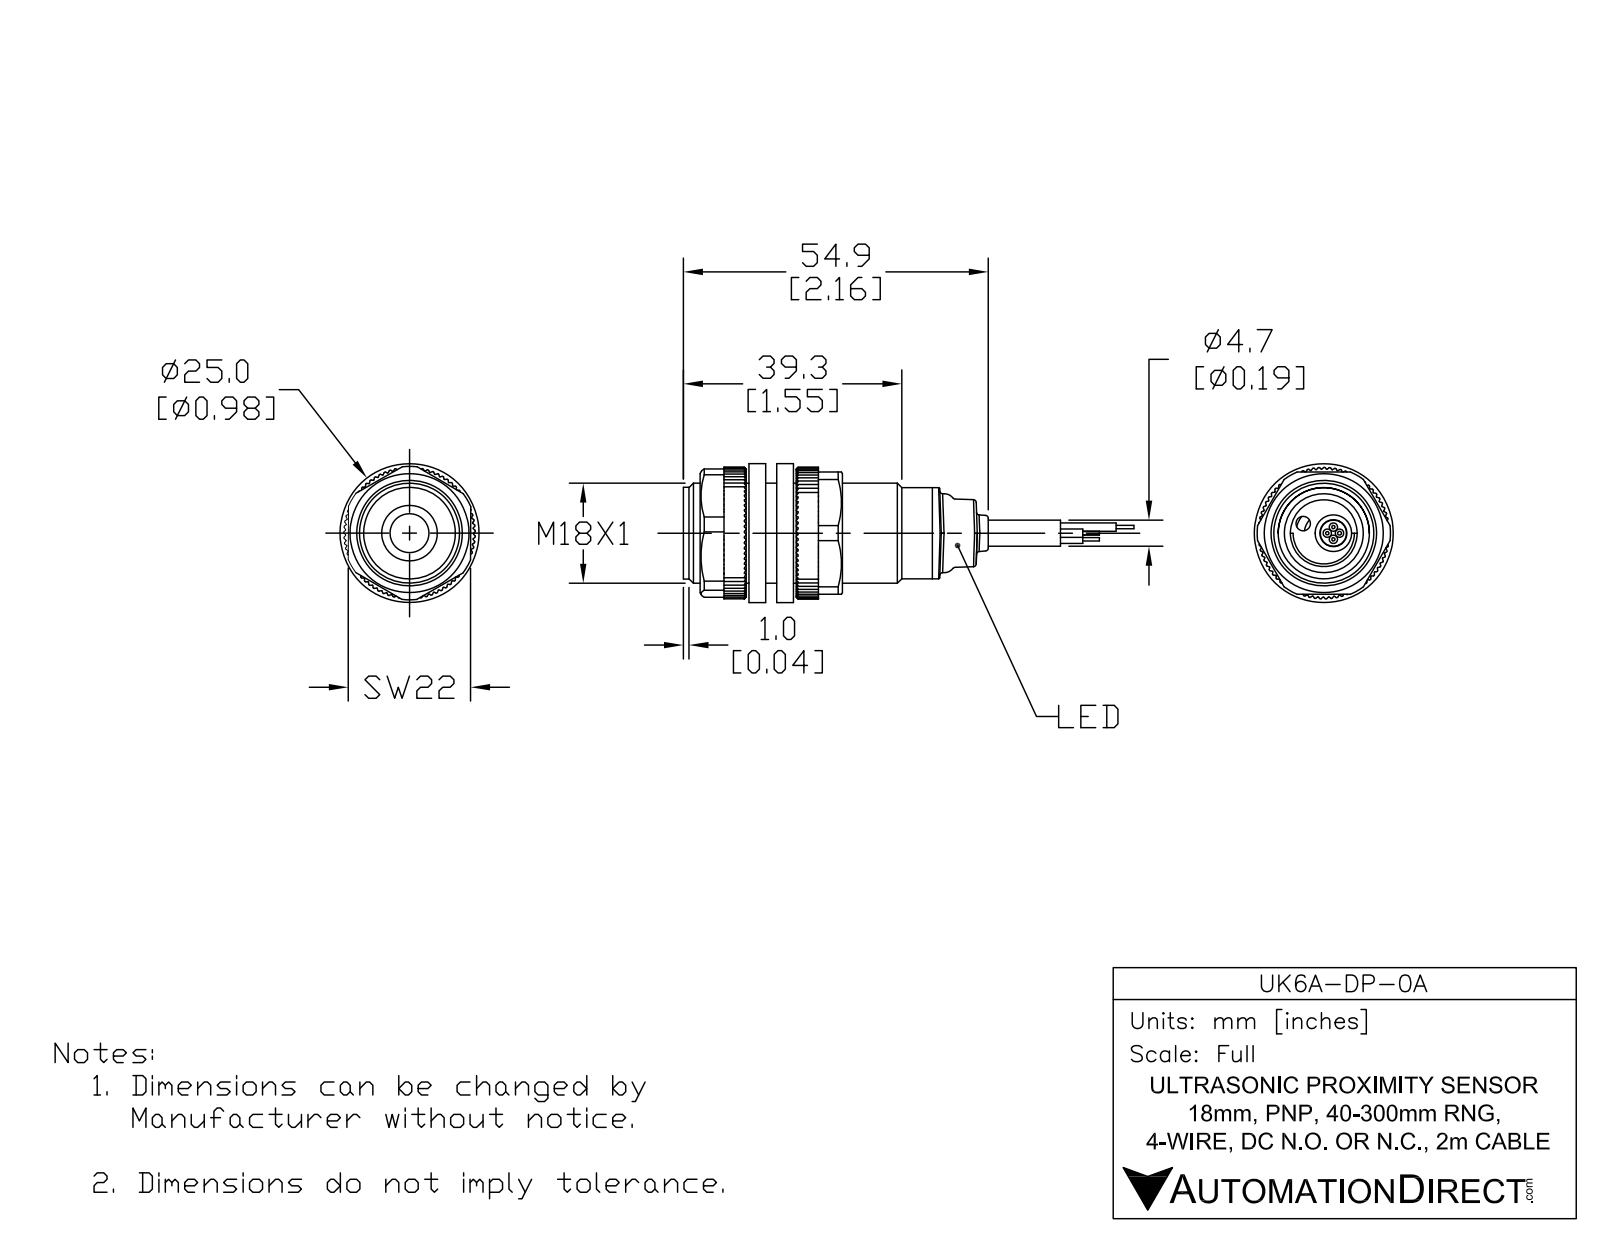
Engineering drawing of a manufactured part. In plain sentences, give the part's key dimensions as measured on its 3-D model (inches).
The part is named "UK6A-DP-0A". Its 3-D file was written by "SolidWorks 2017 (AUTOMOTIVE_DESIGN)". It is 4 solids with 62 faces: 14 planar, 19 cylindrical and 29 other. Overall it measures 3.537 by 0.709 by 0.709 inches. Its volume is 0.787 cubic inches and its surface area 7.432 square inches. Round holes: 1 of diameter 0.185, 1 of diameter 0.374. Round bosses or shafts: 1 of diameter 0.709, 1 of diameter 0.646, 1 of diameter 0.622, 1 of diameter 0.559. Partial cylindrical surfaces (rounded edges, fillets, slot ends): 1 of radius 0.008, 1 of radius 0.02. The main face-to-face distances are 1.724, 0.039, 1.764, 0.039, 1.763, 1.963, 1.962, 1.923, 0.199, 0.255. The hole center spacings are 0.068.
